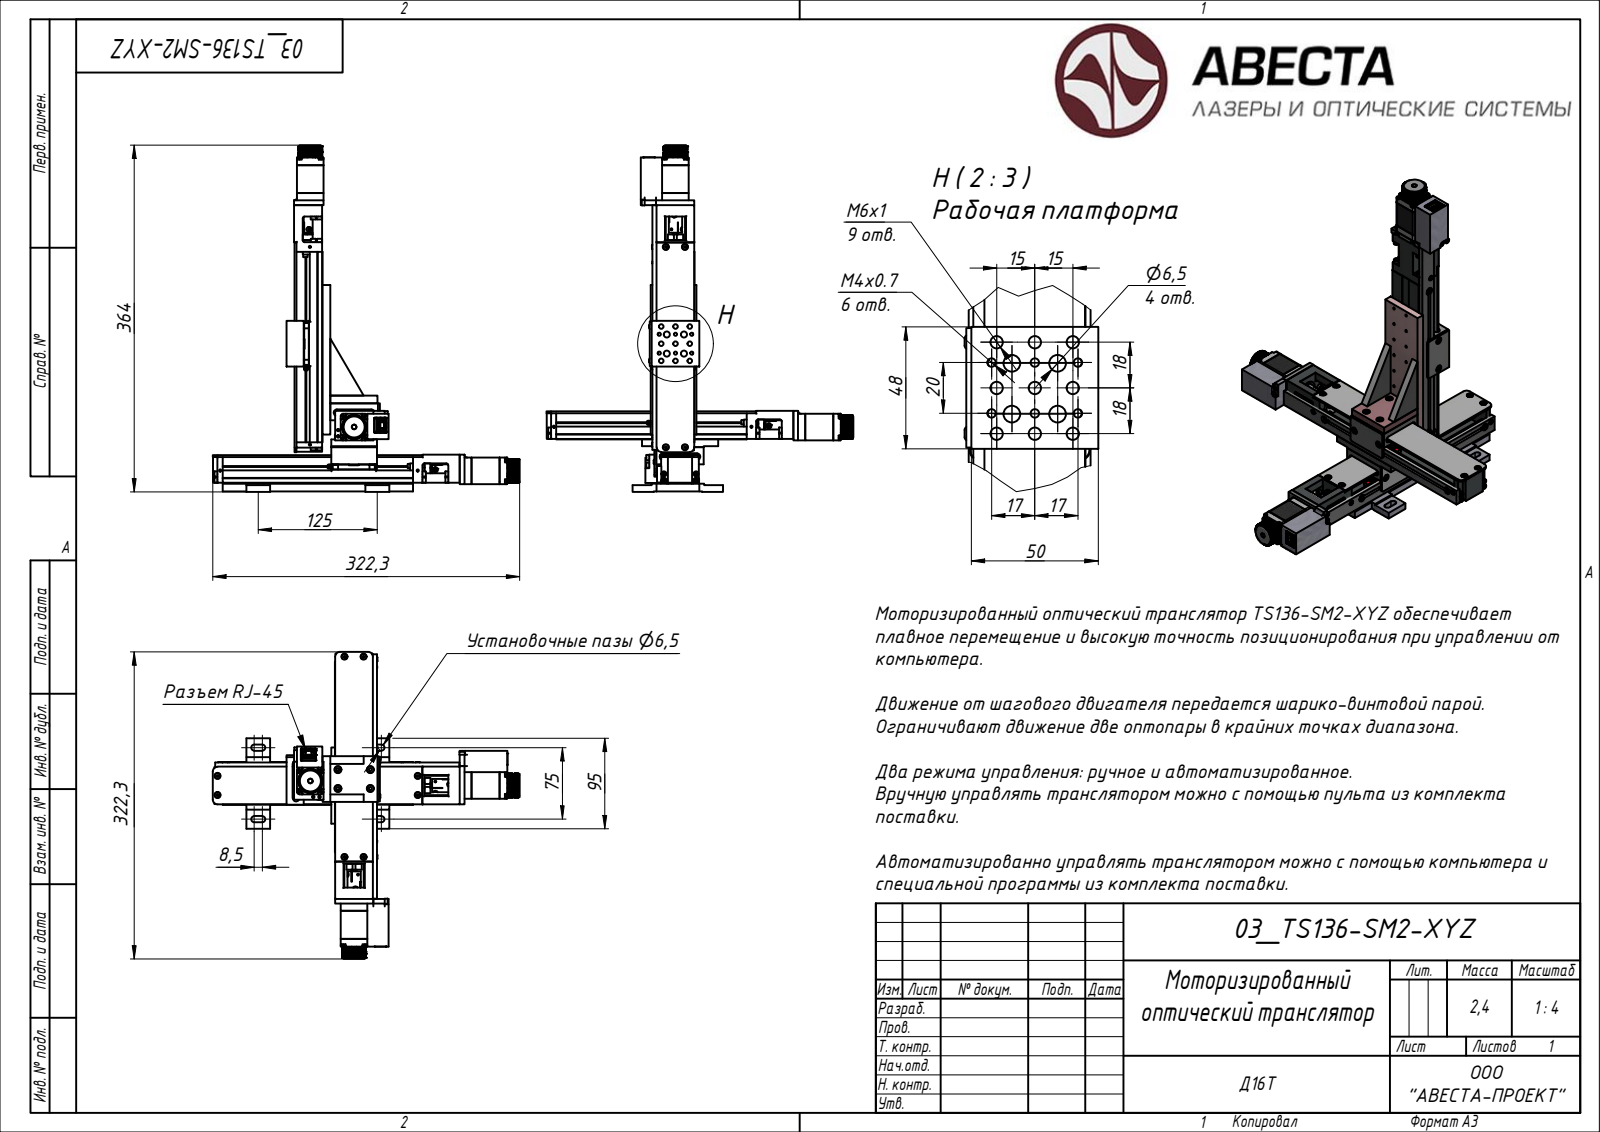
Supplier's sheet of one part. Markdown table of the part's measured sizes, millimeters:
| quantity | value |
| --- | --- |
| STEP written by | Rhino 7.34 (AUTOMOTIVE_DESIGN) |
| units | millimeters |
| bodies | 1 solid, 6762 faces (4180 planar, 1991 cylindrical, 591 other) |
| overall size | 364 × 322.3 × 322.3 |
| volume | 930 856 mm³ |
| surface area | 389 675 mm² |
| round holes (diameter × count) | 6.5 × 42, 3.4 × 30, 7.5 × 22, 3.24 × 21, 2.46 × 18, 2.5 × 17, 1.05 × 15, 2.46 × 13, 4.92 × 13, 2.2 × 12, 3.8 × 12, 5 × 12 |
| round bosses / shafts (diameter × count) | 4.5 × 30, 5.5 × 18, 5.3 × 12, 2.5 × 12, 6 × 11, 3 × 10, 5 × 9, 7 × 6 |
| partial cylindrical surfaces (radius × count) | 0.5 × 108, 3 × 34, 2.5 × 30, 2 × 24, 1 × 12, 3.25 × 8, 1.75 × 6, 2.4 × 6 |
| main face-to-face distances | 46, 2, 0.5, 27.5, 8, 29.5, 5, 24.5, 4.77, 48 |
| hole center spacings | 20, 18, 1, 16.26, 23, 297, 2, 9 |
